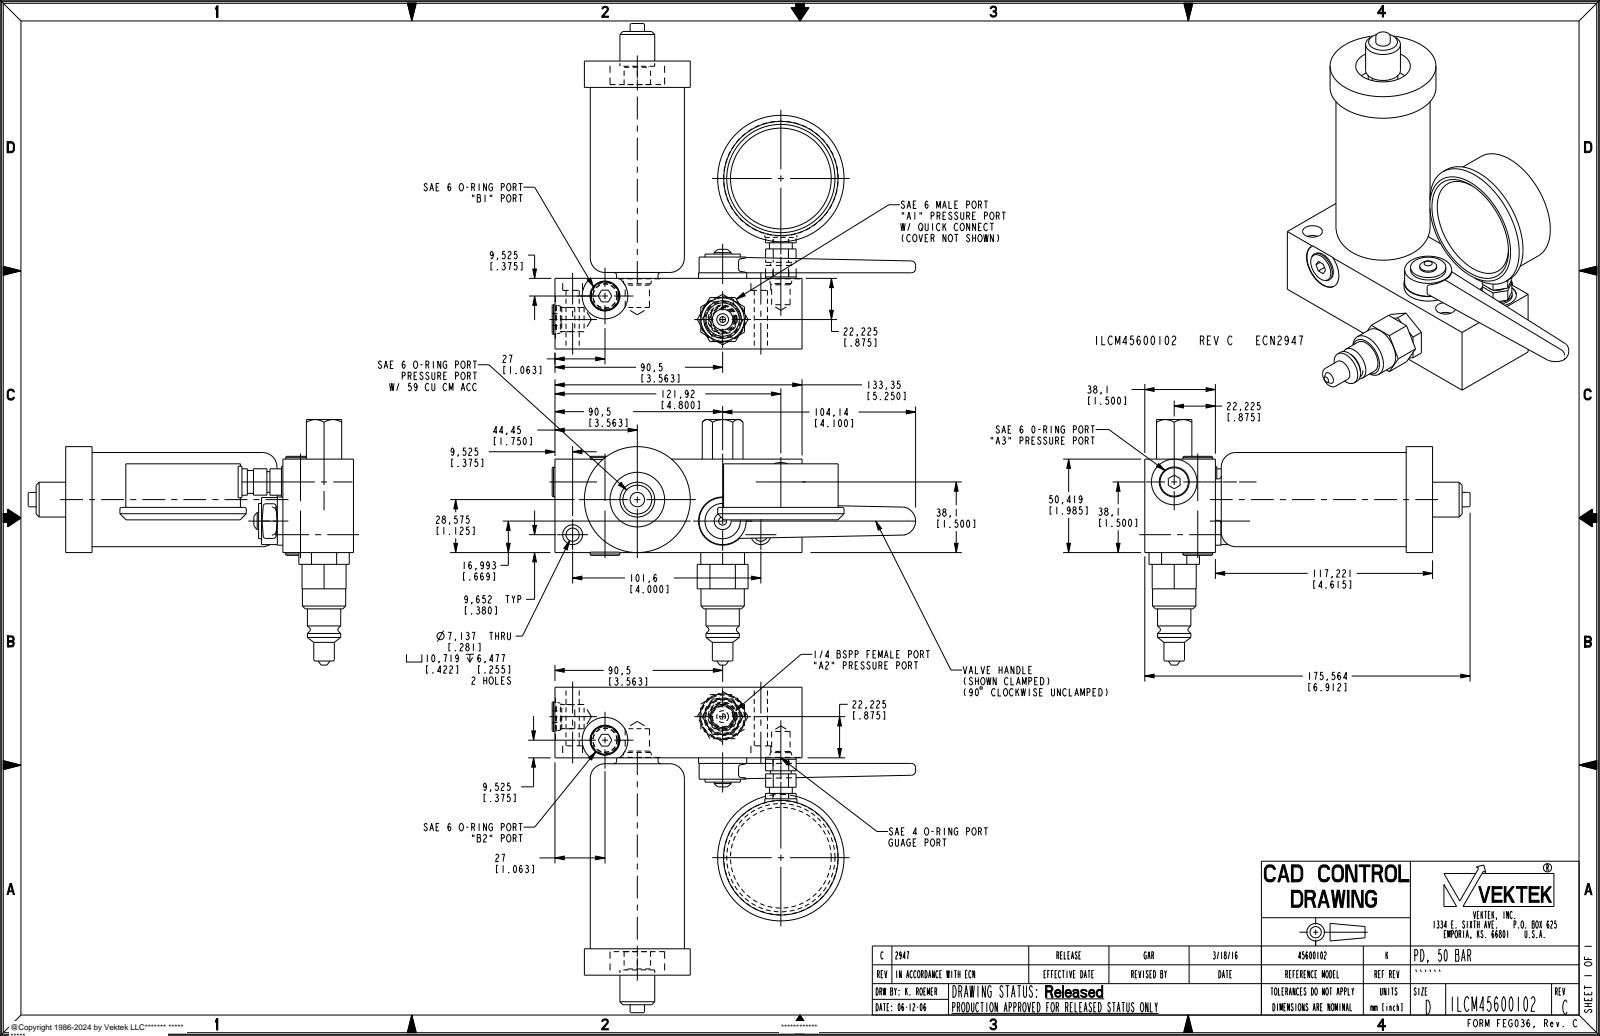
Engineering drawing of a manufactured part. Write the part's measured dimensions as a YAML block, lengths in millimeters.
part_name: "ILCM45600102"
step_written_by: "PRO/ENGINEER BY PARAMETRIC TECHNOLOGY CORPORATION, 2013320 (AUTOMOTIVE_DESIGN)"
units: millimeters
bodies: {solids: 5, faces: 342, planar: 145, cylindrical: 93, other: 104}
overall_size: [196.14, 175.56, 132.44]
volume: 613351
surface_area: 89993
round_holes:
  - {diameter: 13.08, count: 4}
  - {diameter: 24.64, count: 3}
  - {diameter: 7.14, count: 2}
  - {diameter: 10.72, count: 2}
  - {diameter: 9.96, count: 1}
  - {diameter: 11.89, count: 1}
  - {diameter: 20.95, count: 1}
  - {diameter: 29.46, count: 1}
round_bosses_or_shafts:
  - {diameter: 14.29, count: 4}
  - {diameter: 12.95, count: 2}
  - {diameter: 68.2, count: 1}
  - {diameter: 61.85, count: 1}
  - {diameter: 57.15, count: 1}
  - {diameter: 50.8, count: 1}
  - {diameter: 26.01, count: 1}
  - {diameter: 25.4, count: 1}
partial_cylinders:
  - {radius: 2.29, count: 2}
  - {radius: 7.62, count: 1}
  - {radius: 12.32, count: 1}
face_to_face_distances: [38.1, 50.42, 2.54, 47.88, 19.69, 30.73, 28.19, 117.22, 155.32, 133.34]
hole_center_spacings: [30.43, 39.72, 64.76, 69.31, 78.05, 101.6, 115.93]
